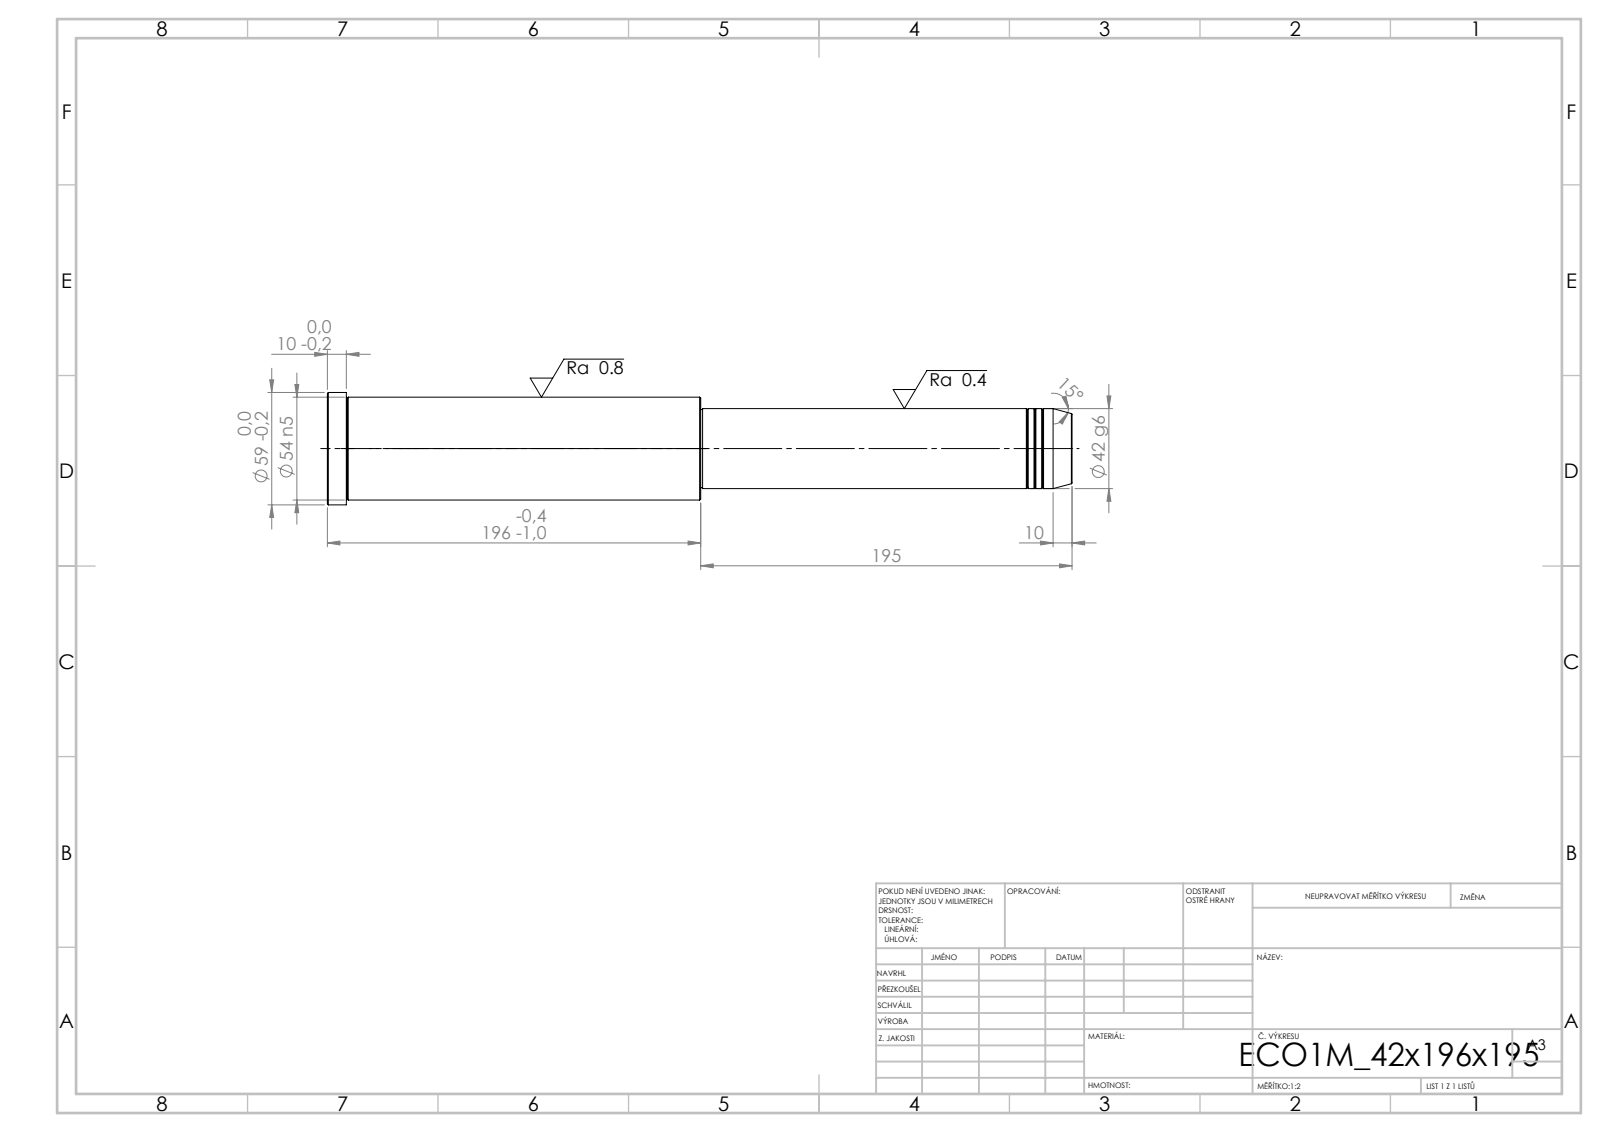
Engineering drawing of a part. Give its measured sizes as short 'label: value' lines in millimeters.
written by: SolidWorks 2019 (CONFIG_CONTROL_DESIGN)
unit: mm
bodies: 1 solid, 43 faces (5 planar, 14 cylindrical, 24 other)
size: 391 × 59 × 59
volume: 721 457 mm³; area: 64 553 mm²
bosses: 1× ⌀59, 1× ⌀54, 1× ⌀42, 1× ⌀41
face distances: 391, 195, 196, 381, 186, 10, 194, 1, 187, 197
